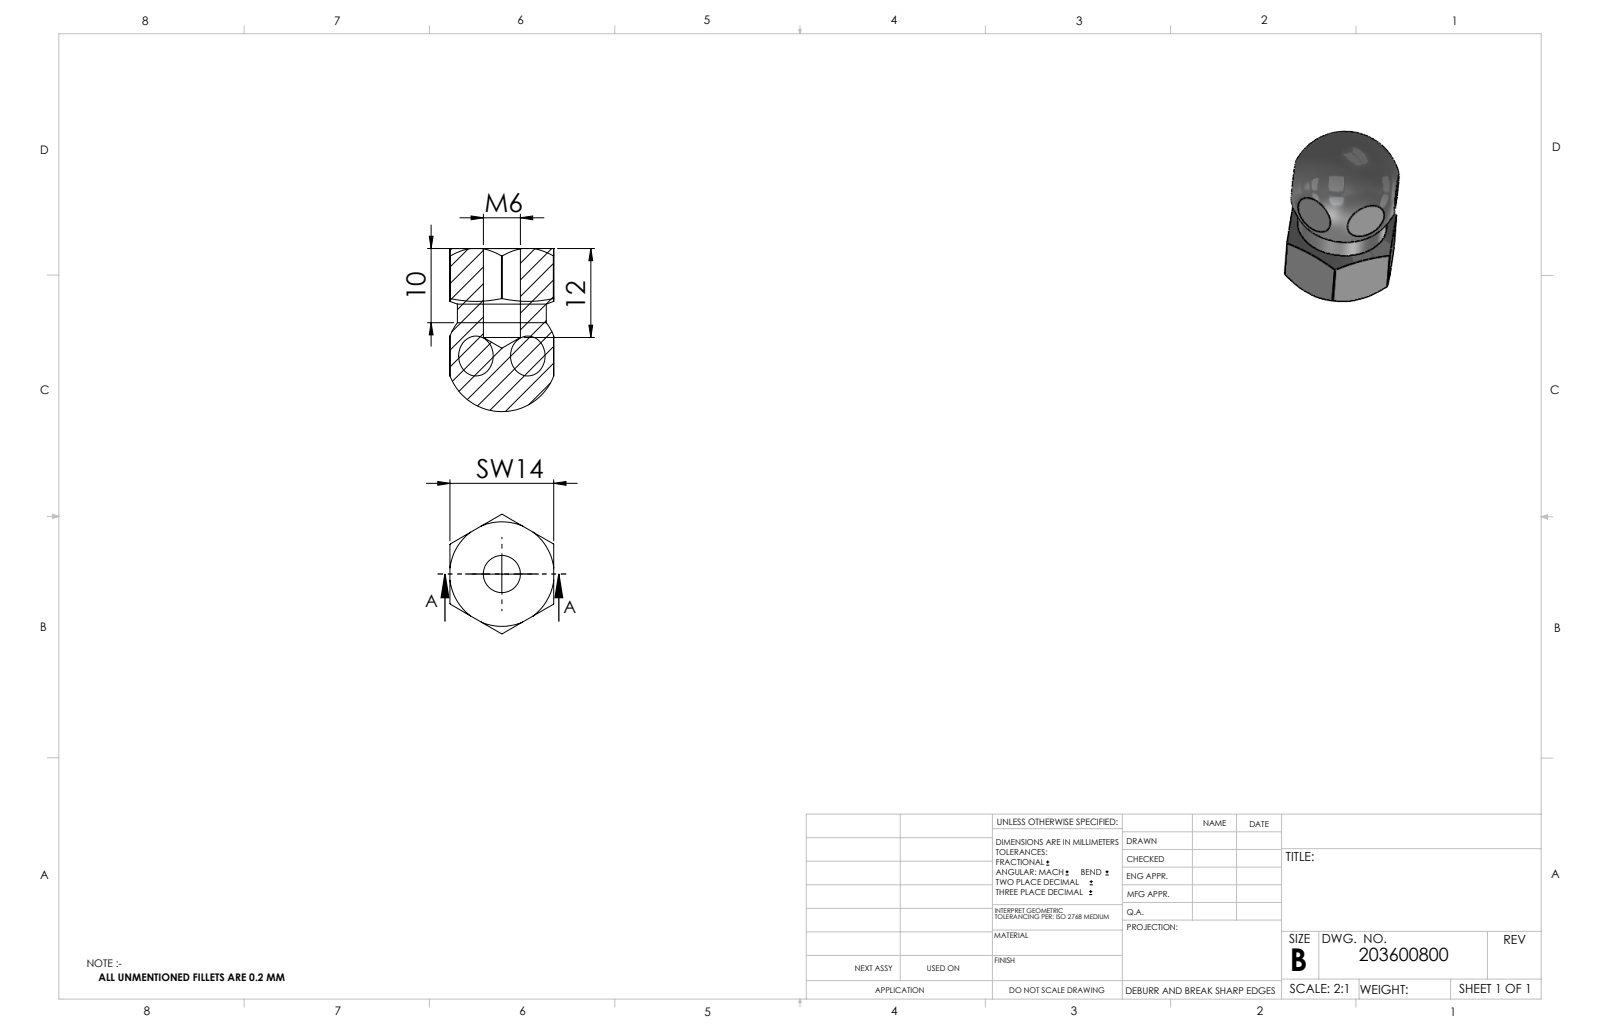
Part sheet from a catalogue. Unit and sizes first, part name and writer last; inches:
Units: inches
Overall size (bounding box): 0.866 × 0.634 × 0.551
Round holes (diameter × count): ⌀0.197 ×1
Round bosses / shafts (diameter × count): ⌀0.472 ×1
Partial cylindrical surfaces — rounded edges, fillets, slot ends (radius × count): R0.317 ×1
Main face-to-face distances: 0.551
Volume: 0.173 in³ · Surface area: 2.178 in²
Bodies: 1 solid, 37 faces (13 planar, 11 cylindrical, 13 other)
Part name (STEP PRODUCT): 203600800_c_1
STEP written by: SolidWorks 2014 (CONFIG_CONTROL_DESIGN)
